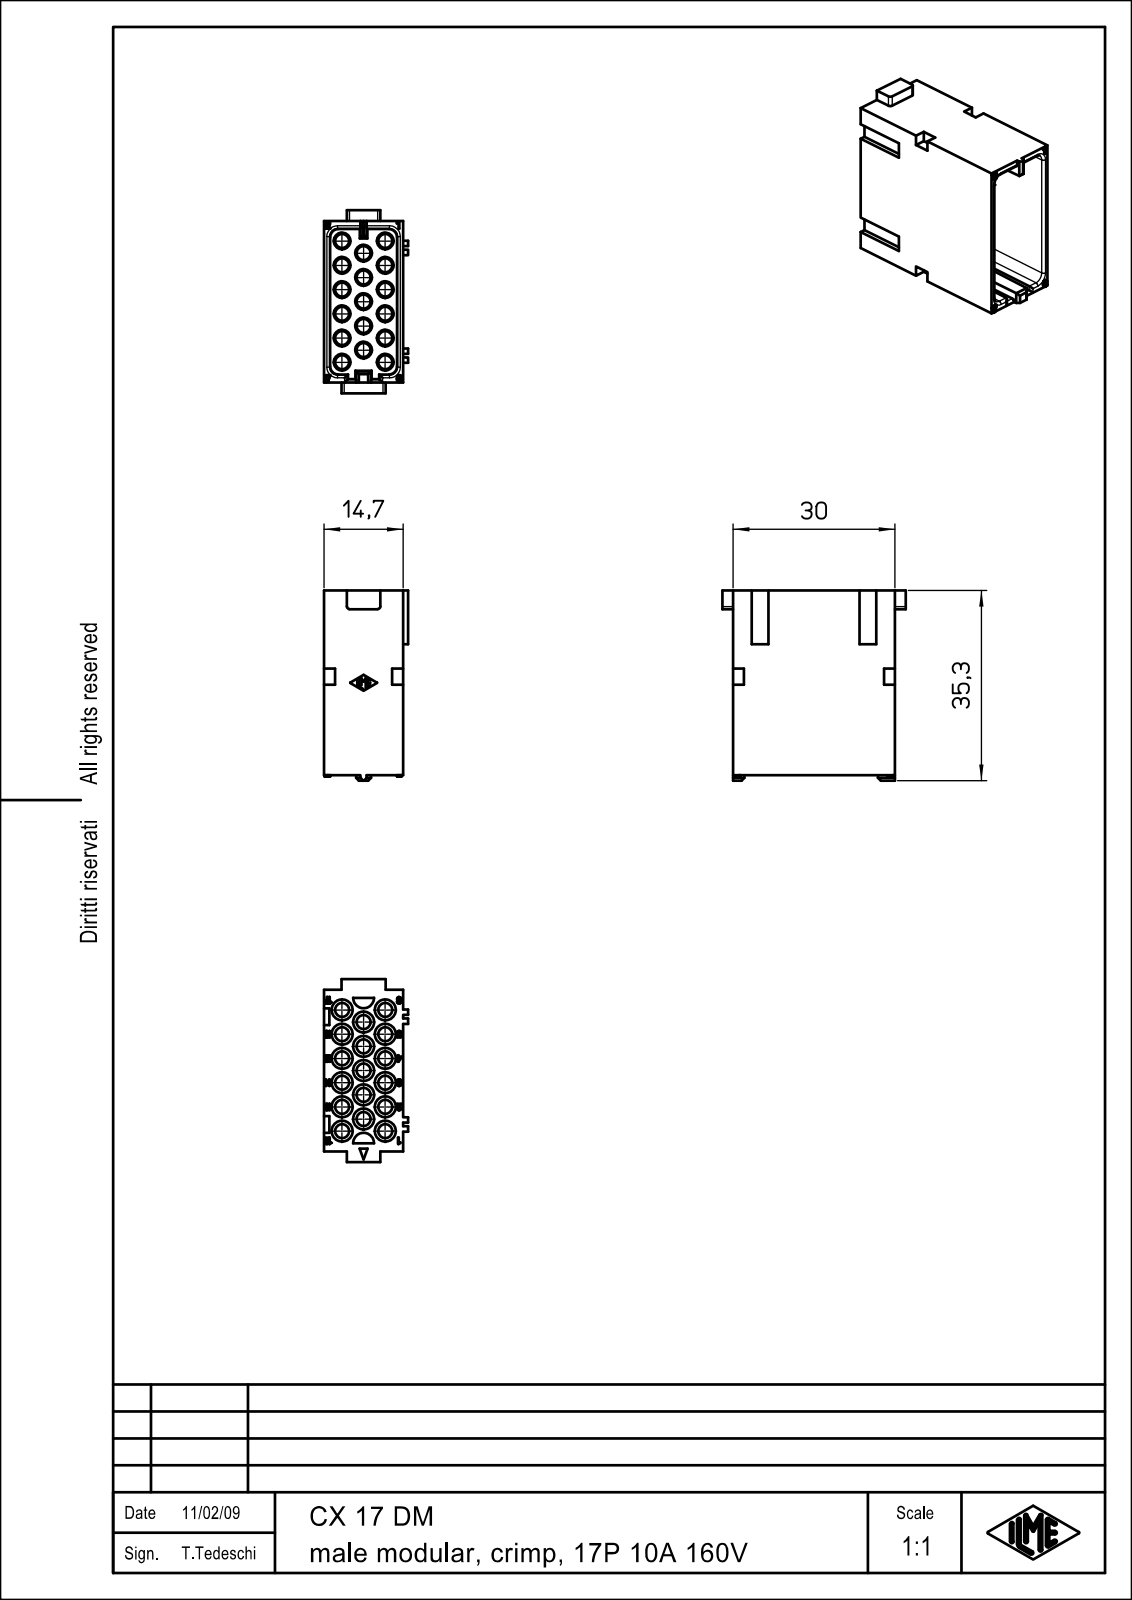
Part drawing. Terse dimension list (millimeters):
name: CX_17_DM
written by: PTC Creo Elements/Direct Modeling 19.0E 27-Jun-2016 (C) Parametric Technology GmbH (AUTOMOTIVE_DESIGN)
unit: mm
bodies: 1 solid, 1124 faces (982 planar, 127 cylindrical, 15 other)
size: 35.3 × 34 × 15.6
volume: 6 433 mm³; area: 9 596 mm²
holes: 17× ⌀2.6, 17× ⌀3.1, 17× ⌀3.9
rounds: 14× R0.1, 5× R0.5, 4× R1.5, 2× R1.95
face distances: 14.7, 30, 20.3, 1.5, 28.5, 1, 3.9, 16.4, 0.9, 3.5
hole spacings: 4.59, 7.85, 4.5, 11.94, 9, 9.18, 12.04, 13.5
